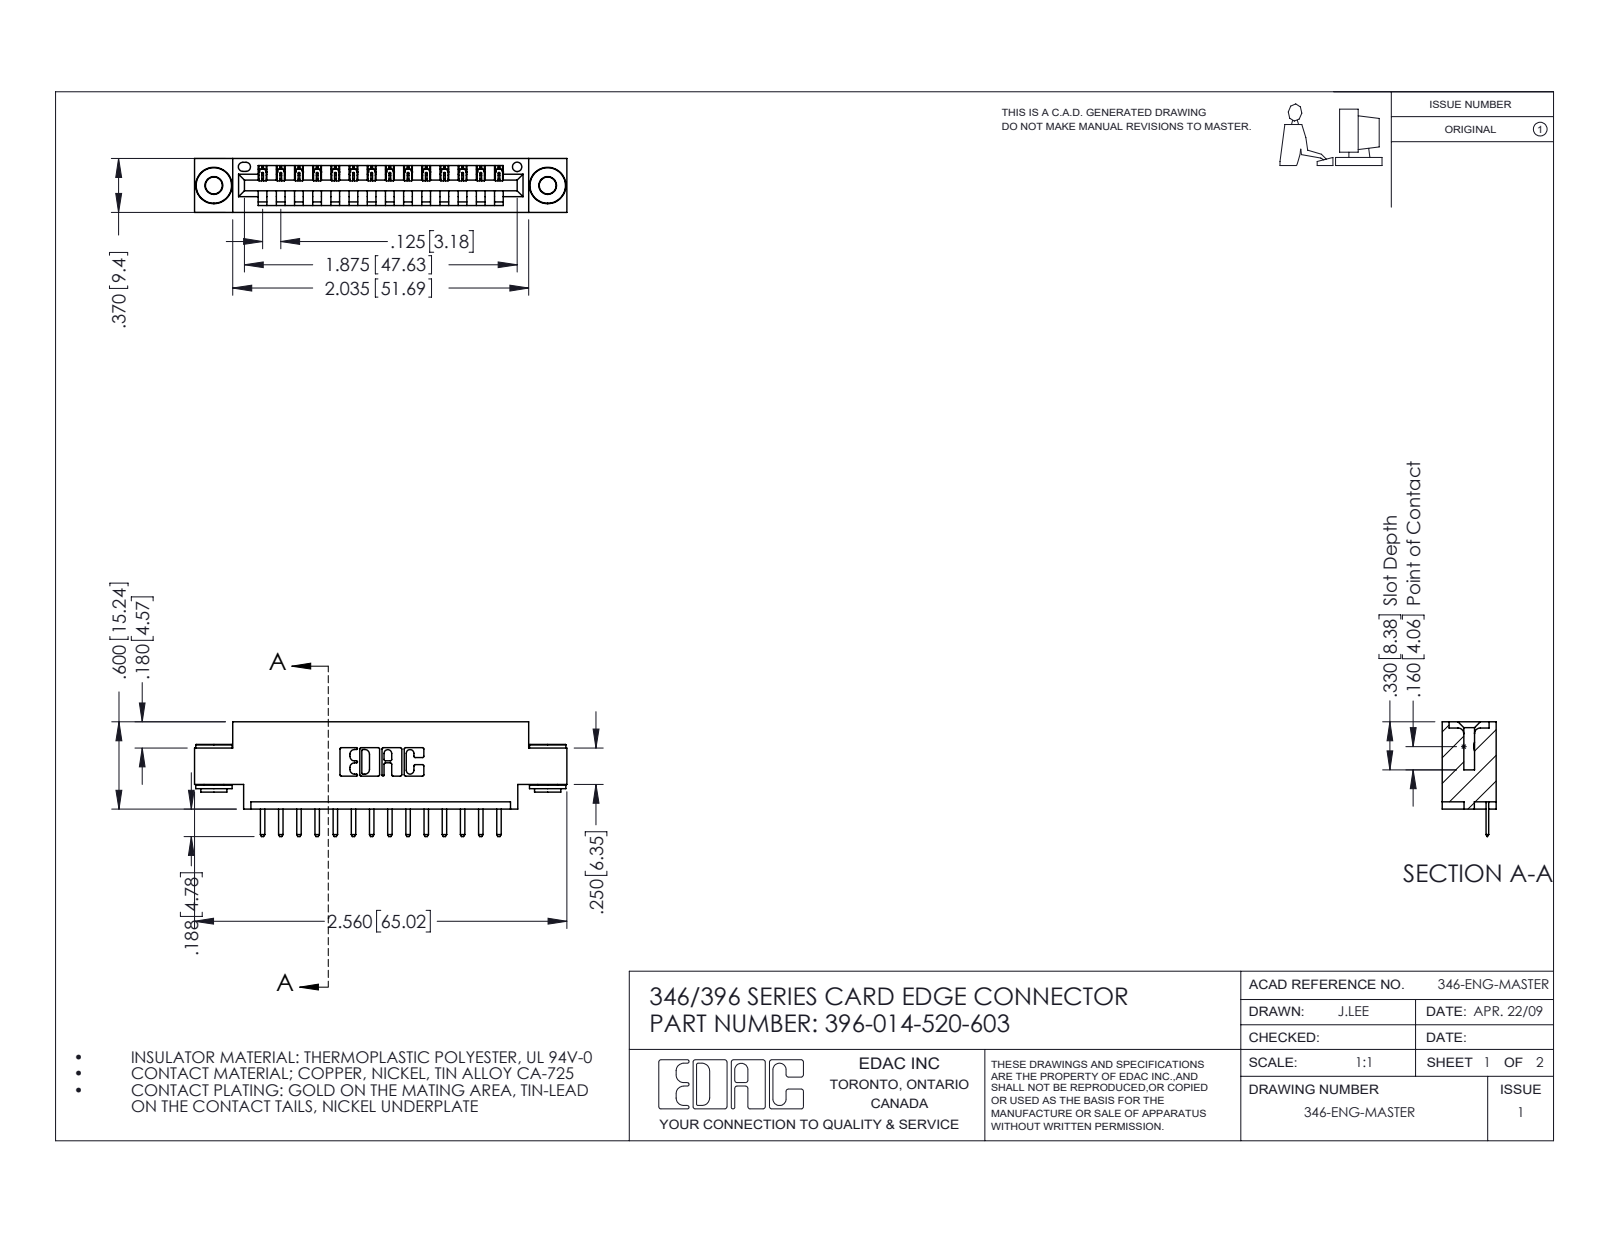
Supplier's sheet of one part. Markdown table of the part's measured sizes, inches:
| quantity | value |
| --- | --- |
| part name | 346 Part_0.170 Offset - 0.156 Dia-TH; 345-292-001_345-293-120; 345-250-002_345-250-002-102; 396-014-520-603 |
| STEP written by | SolidWorks 2016 (CONFIG_CONTROL_DESIGN) |
| units | inches |
| bodies | 17 solids, 1032 faces (678 planar, 346 cylindrical, 8 other) |
| overall size | 2.56 × 0.788 × 0.37 |
| volume | 0.357 in³ |
| surface area | 11.26 in² |
| round holes (diameter × count) | 0.116 × 2, 0.156 × 2, 0.064 × 1 |
| round bosses / shafts (diameter × count) | 0.25 × 2, 0.18 × 2, 0.136 × 2 |
| partial cylindrical surfaces (radius × count) | 0.01 × 30, 0.006 × 28, 0.01 × 22, 0.007 × 6, 0.031 × 6, 0.026 × 3, 0.031 × 2, 0.04 × 2 |
| main face-to-face distances | 0.37, 0.048, 0.322, 0.25, 0.025, 0.148, 0.222, 0.1, 0.174, 0.072 |
| hole center spacings | 0.246, 2.089, 2.295 |
